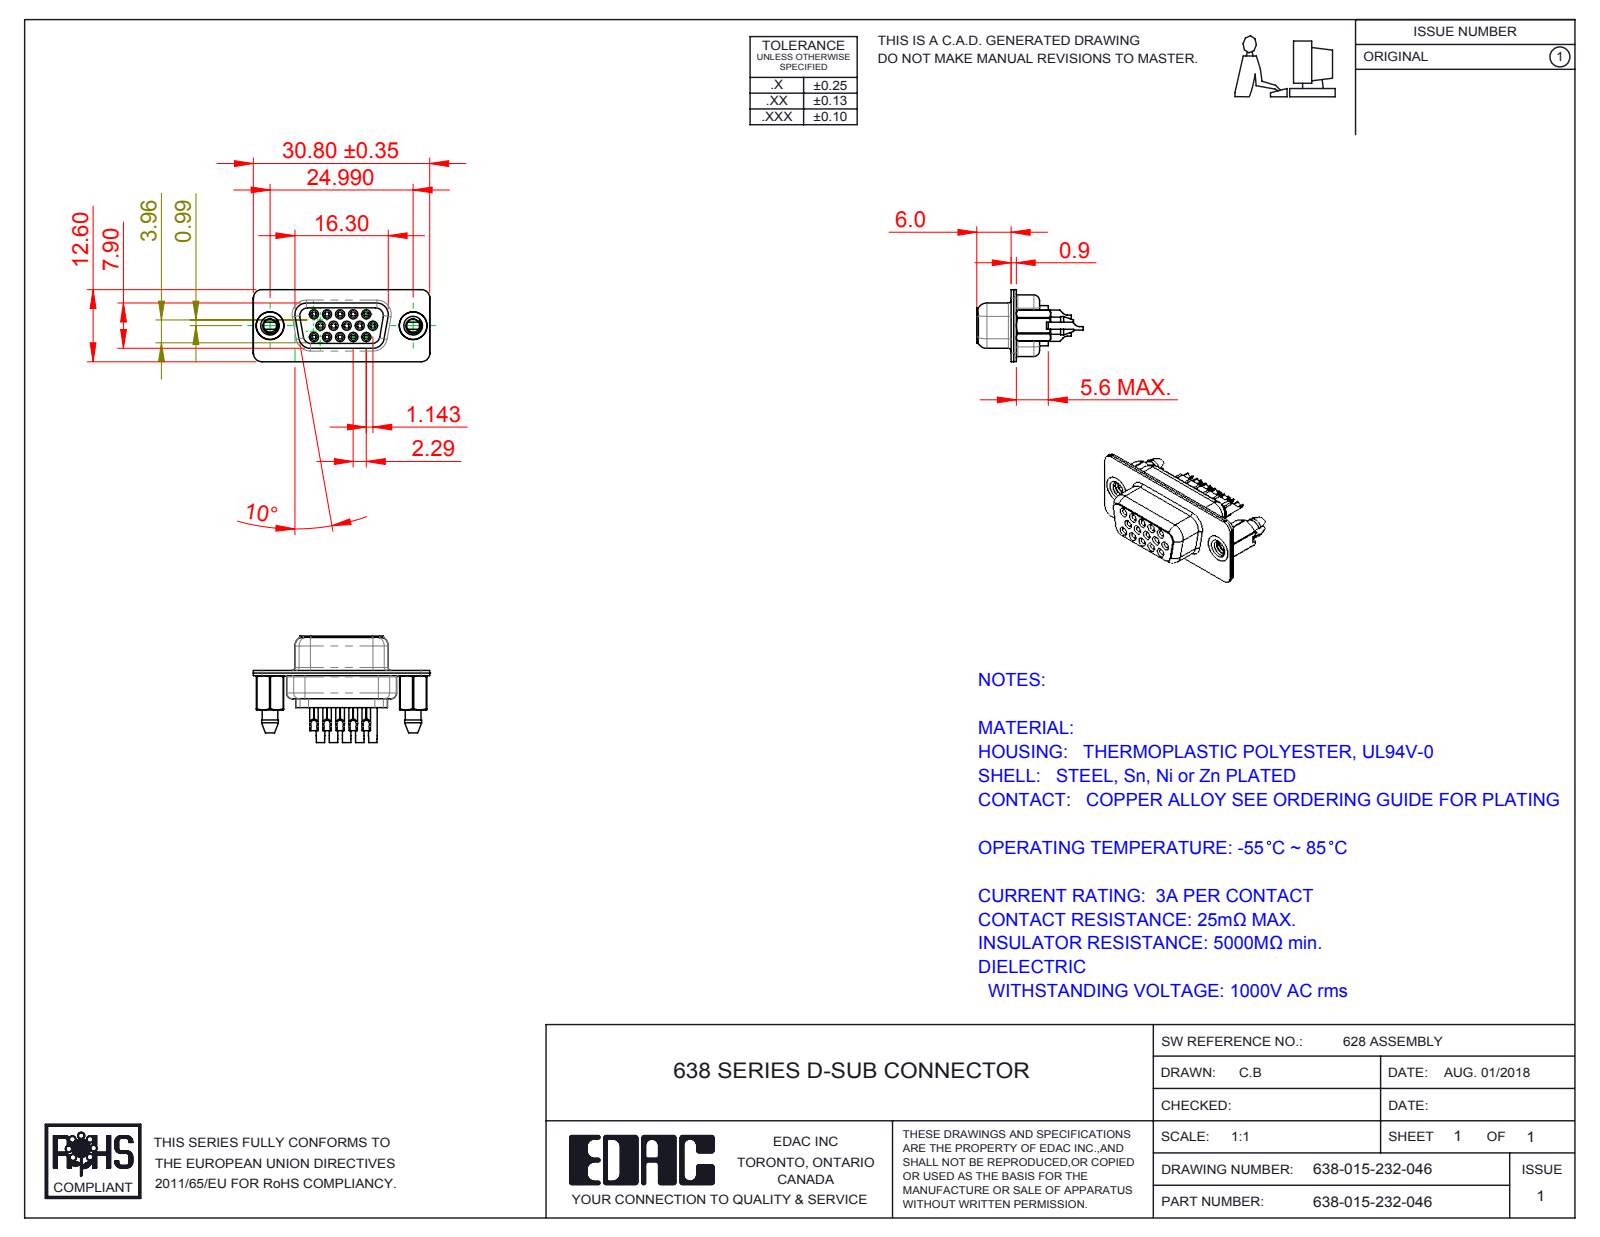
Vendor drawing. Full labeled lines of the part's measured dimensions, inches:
Part name (STEP PRODUCT): 638 Shell Front_15 Contacts; 638 Shell Rear_15 Contacts; 638 Contact Row 1_32L; 638-015-232-046 (+4 more)
STEP written by: SolidWorks 2016 (CONFIG_CONTROL_DESIGN)
Units: inches
Bodies: 20 solids, 1688 faces (414 planar, 544 cylindrical, 730 other)
Overall size (bounding box): 1.213 × 0.732 × 0.496
Volume: 0.105 in³ · Surface area: 9.526 in²
Round holes (diameter × count): ⌀0.031 ×15, ⌀0.039 ×15, ⌀0.043 ×15, ⌀0.063 ×15, ⌀0.067 ×15, ⌀0.071 ×15, ⌀0.079 ×2, ⌀0.089 ×2, ⌀0.157 ×2, ⌀0.159 ×2, ⌀0.191 ×2
Round bosses / shafts (diameter × count): ⌀0.079 ×15, ⌀0.059 ×15, ⌀0.047 ×15, ⌀0.195 ×2, ⌀0.189 ×2
Partial cylindrical surfaces — rounded edges, fillets, slot ends (radius × count): R0.059 ×22, R0.079 ×12, R0.011 ×10, R0.061 ×8, R0.039 ×7, R0.053 ×5, R0.01 ×4, R0.02 ×4
Main face-to-face distances: 0.018, 0.035, 0.016, 0.056, 0.35, 0.26, 0.055, 0.236, 0.09, 0.187
Hole centre spacings: 0.156, 0.09, 0.18, 0.09, 0.238, 0.238, 0.27, 0.312
